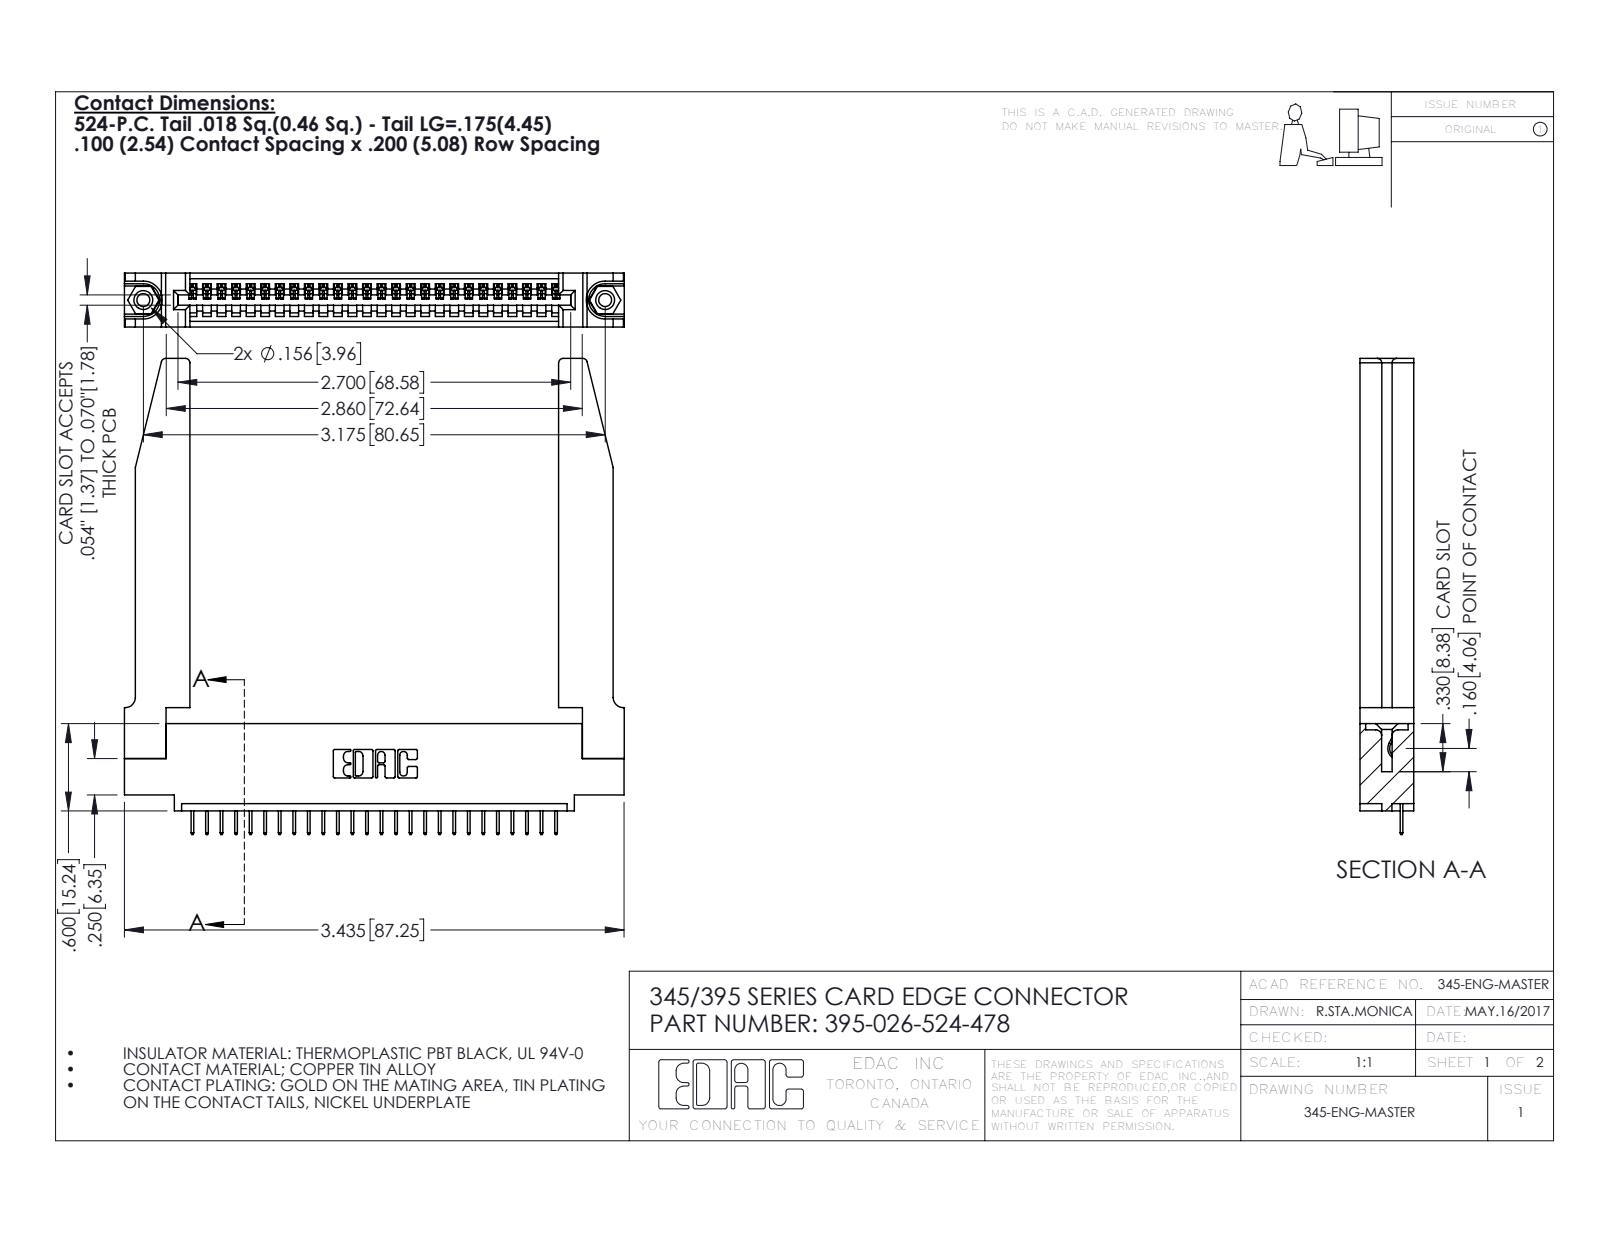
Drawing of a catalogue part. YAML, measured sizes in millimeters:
part_name: "345-292-001_345-293-124; 345 Part_0.110 Offset - 0.156 Dia-TH; 345-220-078_345-220-078; 395-026-524-478 (+1 more)"
step_written_by: "SolidWorks 2016 (CONFIG_CONTROL_DESIGN)"
units: millimeters
bodies: {solids: 31, faces: 1976, planar: 1422, cylindrical: 502, other: 52}
overall_size: [87.3, 83.1, 9.4]
volume: 15700
surface_area: 16990
round_holes:
  - {diameter: 2.3, count: 2}
  - {diameter: 3.2, count: 2}
  - {diameter: 4, count: 2}
  - {diameter: 1.6, count: 1}
round_bosses_or_shafts:
  - {diameter: 3.9, count: 2}
partial_cylinders:
  - {radius: 0.2, count: 52}
  - {radius: 0.3, count: 22}
  - {radius: 0.8, count: 8}
  - {radius: 0.2, count: 6}
  - {radius: 0.8, count: 6}
  - {radius: 0.7, count: 3}
  - {radius: 0.8, count: 2}
  - {radius: 1, count: 2}
face_to_face_distances: [9.4, 1.8, 7.6, 5.1, 2.5, 6.9, 0.6, 3.8, 3.8, 5.7]
hole_center_spacings: [6.9, 74.7, 80.6]
